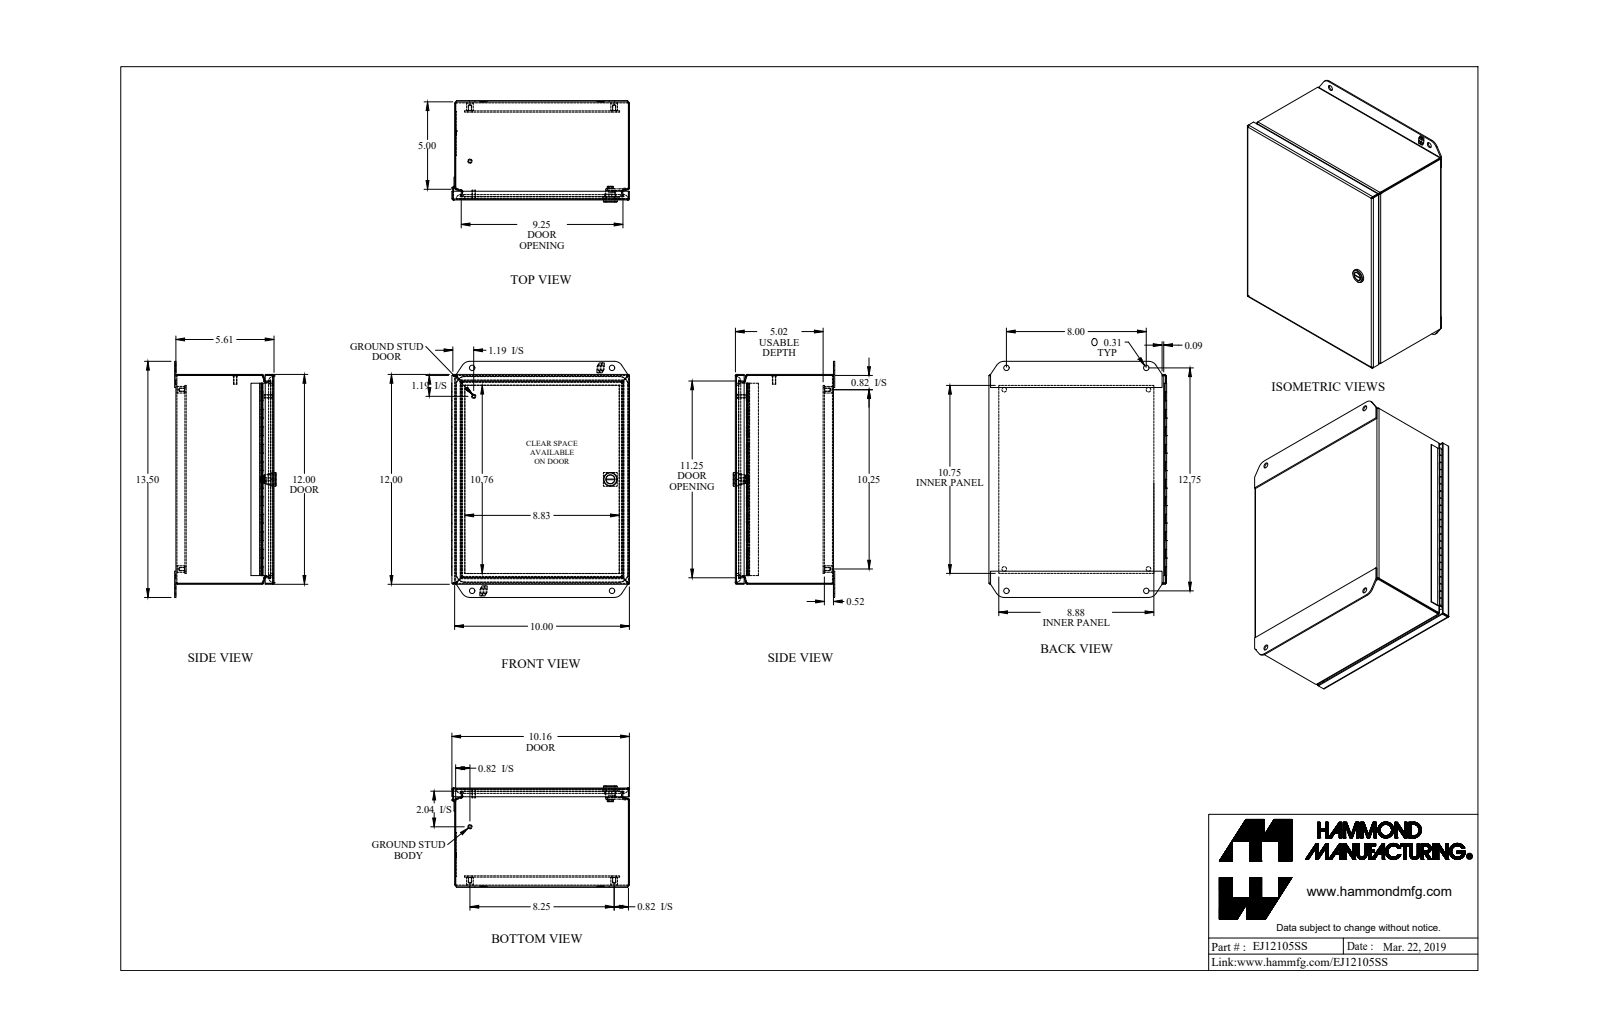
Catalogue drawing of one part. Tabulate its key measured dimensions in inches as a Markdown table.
| quantity | value |
| --- | --- |
| part name | EJ12105SS_Default |
| STEP written by | SolidWorks 2019 (CONFIG_CONTROL_DESIGN) |
| units | inches |
| bodies | 16 solids, 720 faces (402 planar, 222 cylindrical, 96 other) |
| overall size | 13.5 × 10.165 × 5.805 |
| volume | 42.59 in³ |
| surface area | 1 404 in² |
| round holes (diameter × count) | 0.156 × 4, 0.265 × 4, 0.313 × 4, 0.05 × 1, 0.516 × 1 |
| round bosses / shafts (diameter × count) | 0.375 × 4, 0.25 × 2, 0.19 × 2, 0.788 × 1, 0.535 × 1, 0.496 × 1, 0.435 × 1, 0.1 × 1 |
| partial cylindrical surfaces (radius × count) | 0.029 × 16, 0.086 × 16, 0.281 × 12, 0.25 × 4, 0.499 × 4, 0.5 × 4, 0.06 × 2, 0.03 × 1 |
| main face-to-face distances | 0.057, 5.554, 0.072, 0.589, 5.611, 5.497, 9.943, 11.943, 5.094, 5.037 |
| hole center spacings | 1.256, 11.501, 10.25, 8.22, 13.158, 14.081, 5.13, 6.376 |
